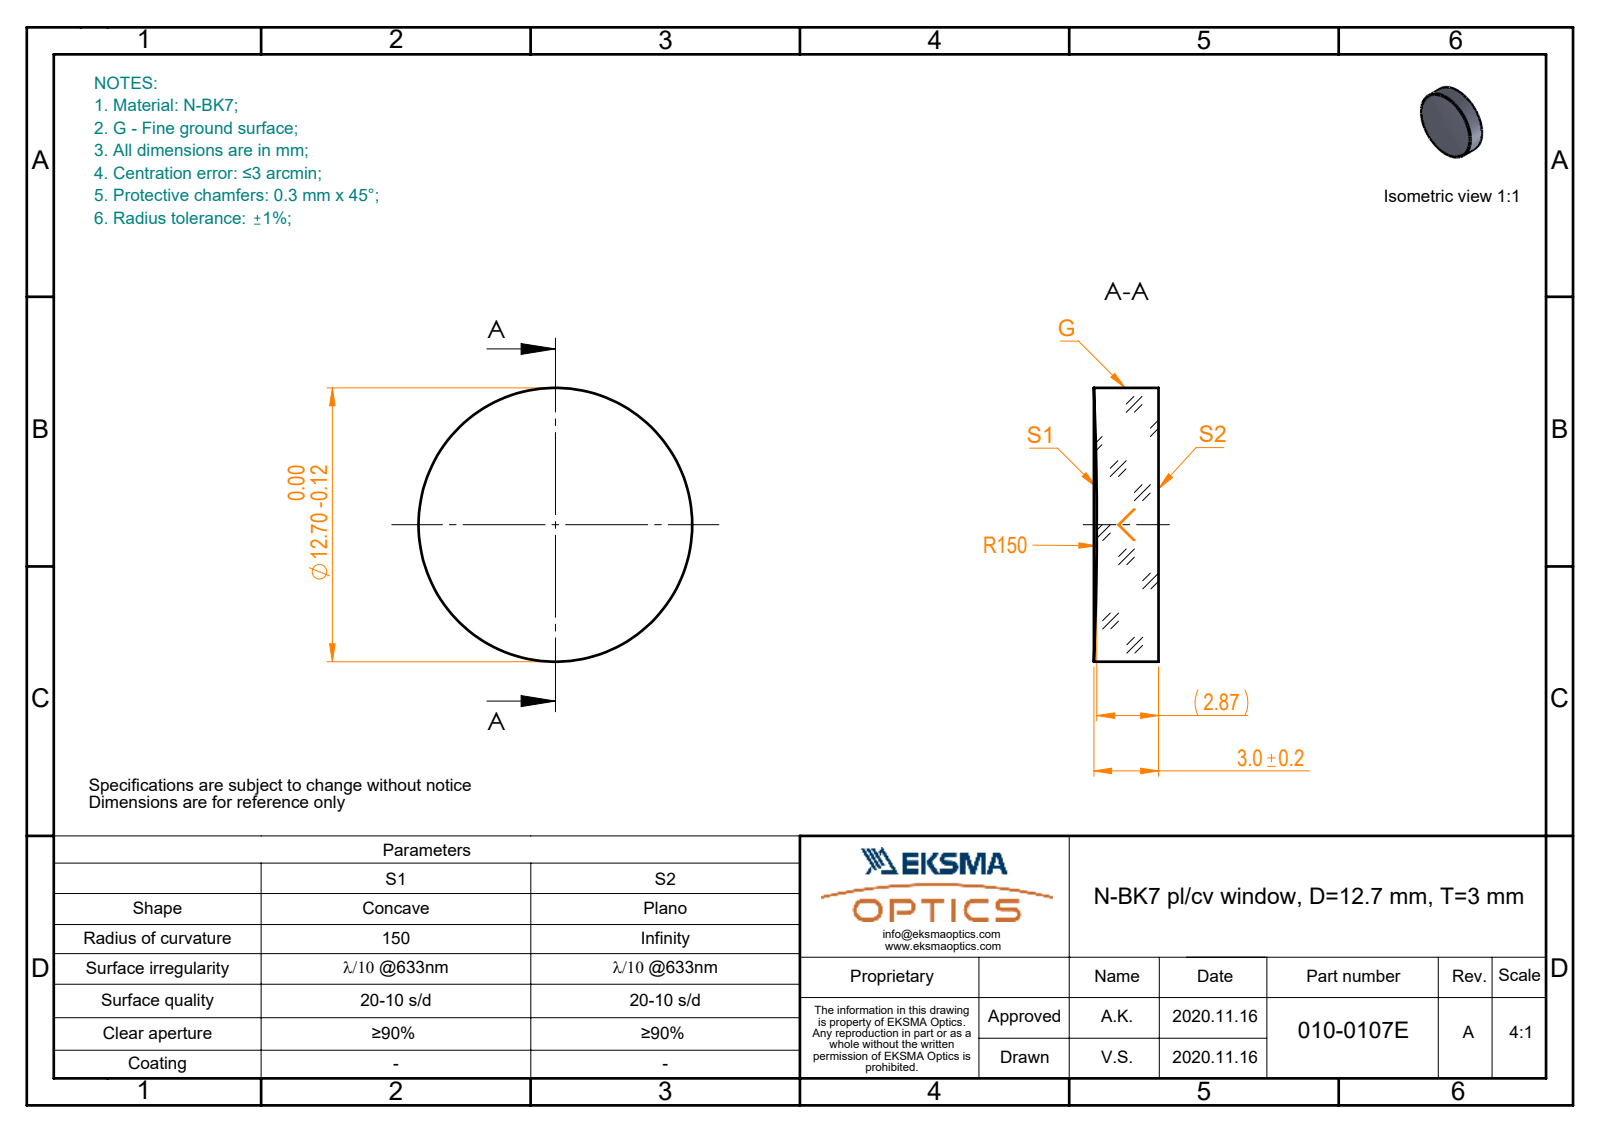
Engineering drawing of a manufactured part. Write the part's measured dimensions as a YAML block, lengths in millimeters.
part_name: "010-0107E_N-BK7_PCV_window"
step_written_by: "SolidWorks 2019 (CONFIG_CONTROL_DESIGN)"
units: millimeters
bodies: {solids: 1, faces: 5, planar: 1, cylindrical: 2, other: 2}
overall_size: [12.7, 12.7, 3]
volume: 372
surface_area: 373
round_bosses_or_shafts:
  - {diameter: 12.7, count: 1}
